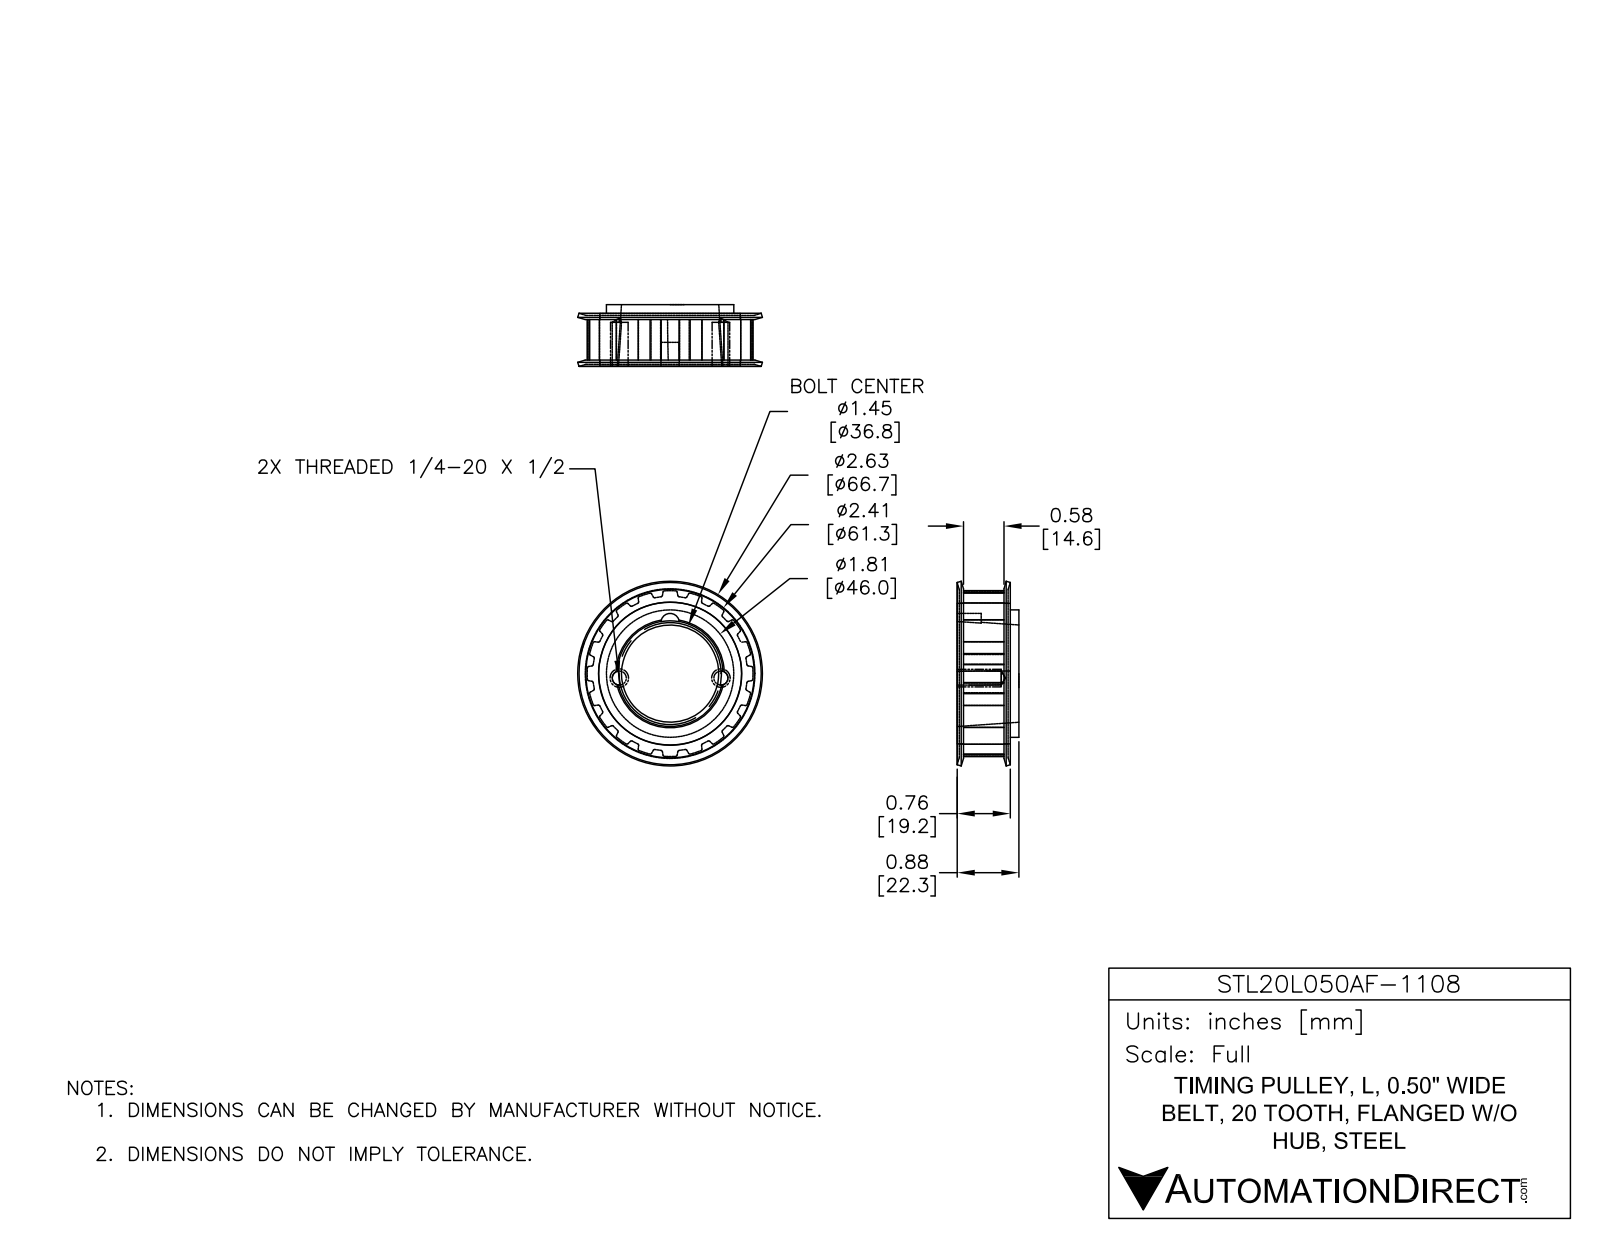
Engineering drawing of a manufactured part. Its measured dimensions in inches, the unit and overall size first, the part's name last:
Units: inches
Overall size (bounding box): 2.625 × 2.625 × 0.878
Round holes (diameter × count): ⌀2.035 ×1
Round bosses / shafts (diameter × count): ⌀2.031 ×1, ⌀1.81 ×1
Partial cylindrical surfaces — rounded edges, fillets, slot ends (radius × count): R0.015 ×40, R0.02 ×40, R0.1 ×2, R0.13 ×1, R1.179 ×1
Main face-to-face distances: 0.06, 0.635, 0.575, 0.663, 0.088, 0.028, 0.695, 0.723, 0.152, 0.213
Volume: 2.063 in³ · Surface area: 26.6 in²
Bodies: 3 solids, 221 faces (70 planar, 133 cylindrical, 18 other)
Part name (STEP PRODUCT): STL20L050AF-1108
STEP written by: SolidWorks 2017 (AUTOMOTIVE_DESIGN)
